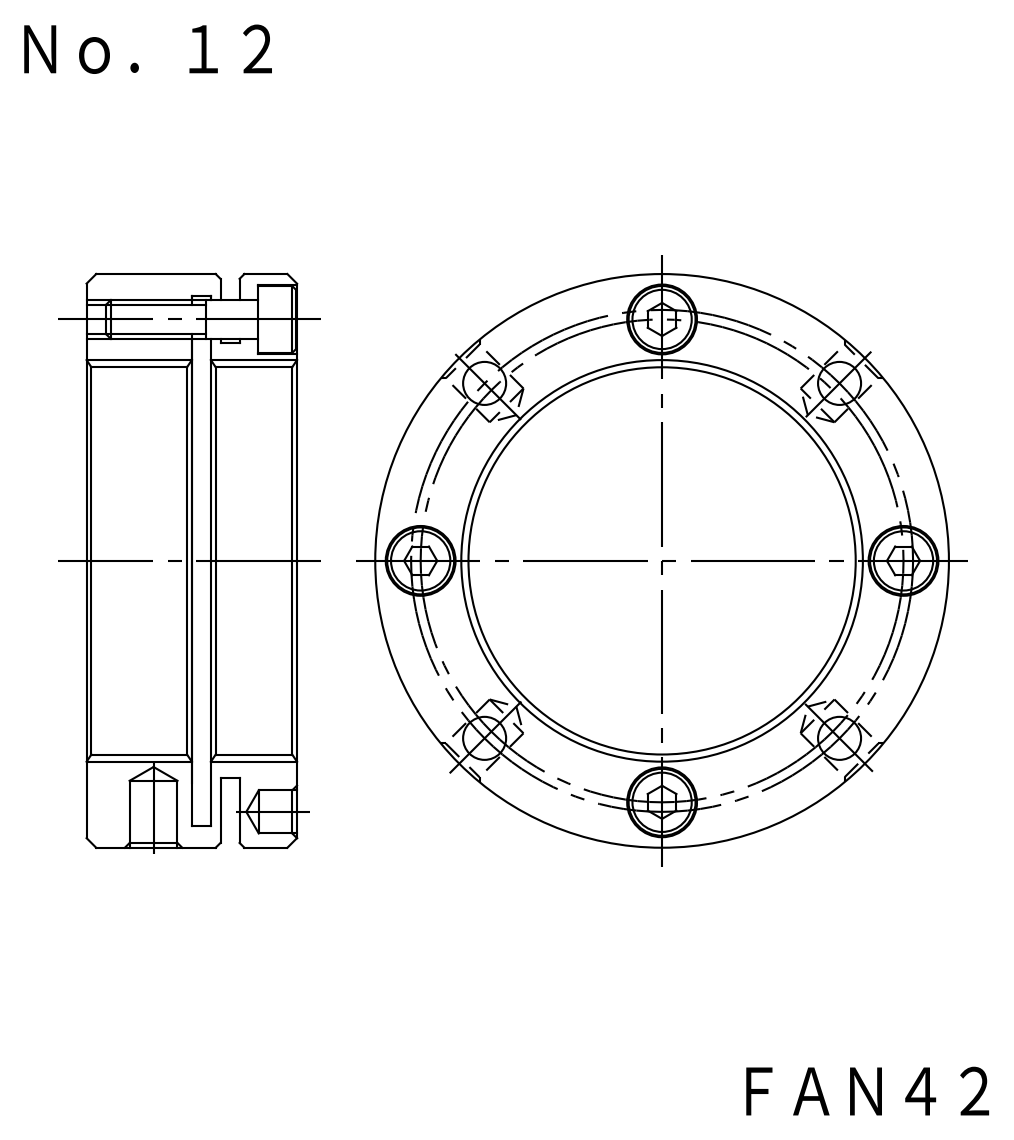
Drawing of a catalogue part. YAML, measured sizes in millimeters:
part_name: "FKD FAN42; M4X16_default"
step_written_by: "SolidWorks 2012 (CONFIG_CONTROL_DESIGN)"
units: millimeters
bodies: {solids: 5, faces: 142, planar: 50, cylindrical: 76, other: 16}
overall_size: [60, 60, 22]
volume: 26595
surface_area: 17247
round_holes:
  - {diameter: 3.24, count: 4}
  - {diameter: 4.3, count: 4}
  - {diameter: 4.5, count: 4}
  - {diameter: 5, count: 4}
  - {diameter: 7.3, count: 4}
  - {diameter: 42, count: 1}
  - {diameter: 56, count: 1}
round_bosses_or_shafts:
  - {diameter: 7, count: 4}
  - {diameter: 4, count: 4}
  - {diameter: 60, count: 1}
  - {diameter: 46, count: 1}
face_to_face_distances: [2, 3, 11, 22, 16, 14, 8, 6, 5, 13]
hole_center_spacings: [19.82, 47.81, 25.5, 26.25, 36.06, 37.12, 51, 52.5]
